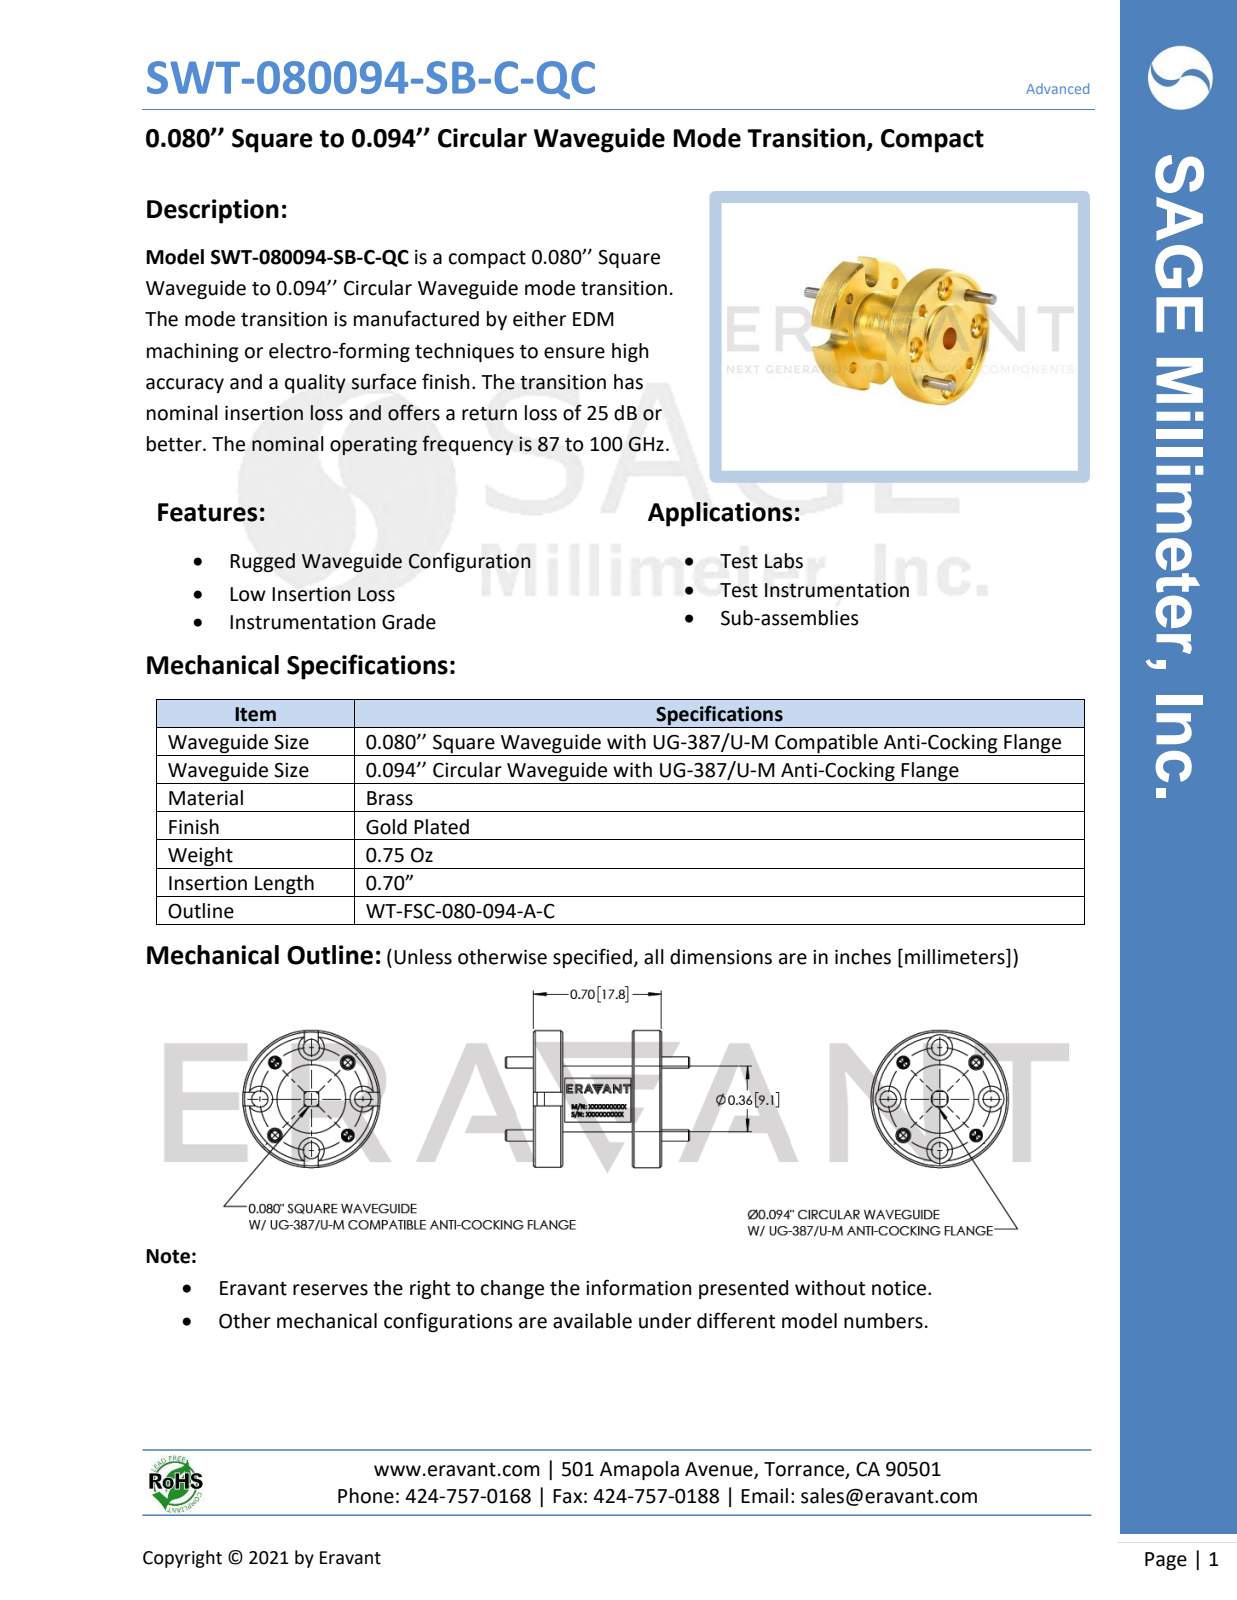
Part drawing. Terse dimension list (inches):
name: WT-FSC-080-094-A-C
written by: SolidWorks 2021 (AUTOMOTIVE_DESIGN)
unit: in
bodies: 5 solids, 175 faces (45 planar, 78 cylindrical, 52 other)
size: 1.005 × 0.75 × 0.75
volume: 0.157 in³; area: 3.445 in²
holes: 4× ⌀0.061, 4× ⌀0.067, 4× ⌀0.089, 4× ⌀0.14, 1× ⌀0.68
bosses: 4× ⌀0.063, 1× ⌀0.75, 1× ⌀0.375, 1× ⌀0.36
face distances: 0.14, 0.52, 0.02, 0.16, 0.54, 0.68, 0.38, 0.66, 0.7, 0.06
hole spacings: 0.215, 0.281, 0.398, 0.519, 0.562
